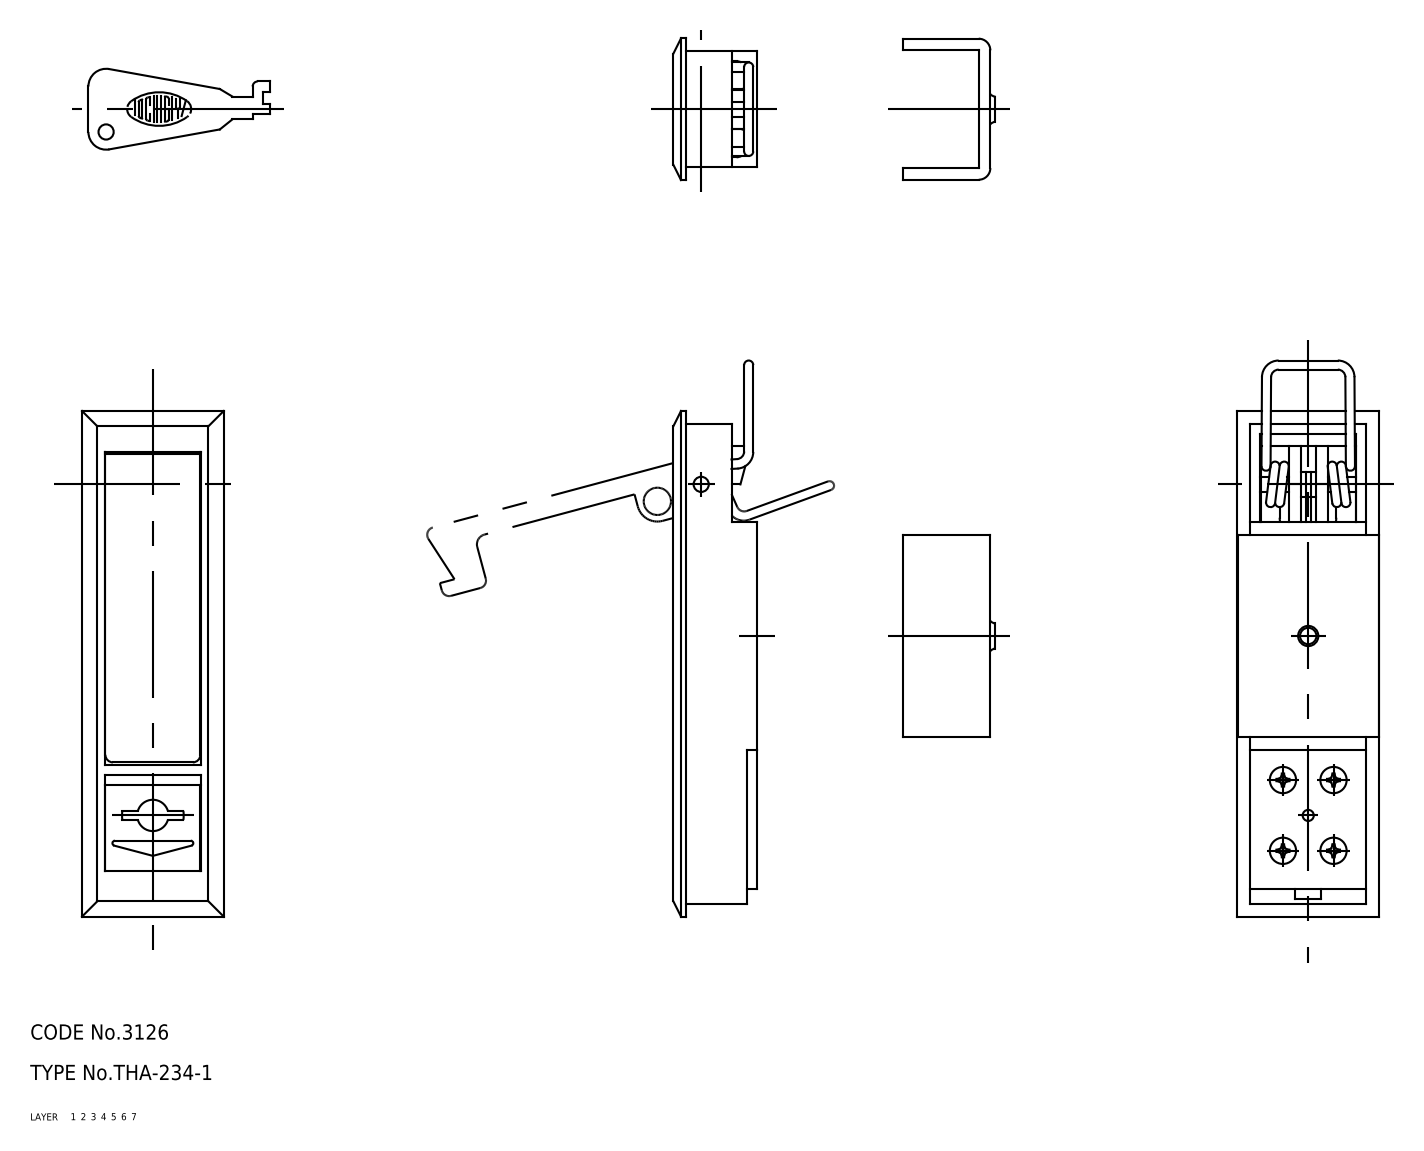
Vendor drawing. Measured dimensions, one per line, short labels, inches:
name: cam; handle; latch; key (+3 more)
written by: CADfix (AUTOMOTIVE_DESIGN)
unit: in
bodies: 6 solids, 373 faces (0 planar, 0 cylindrical, 373 other)
size: 4.331 × 3.013 × 1.102
volume: 1.661 in³; area: 40.18 in²
